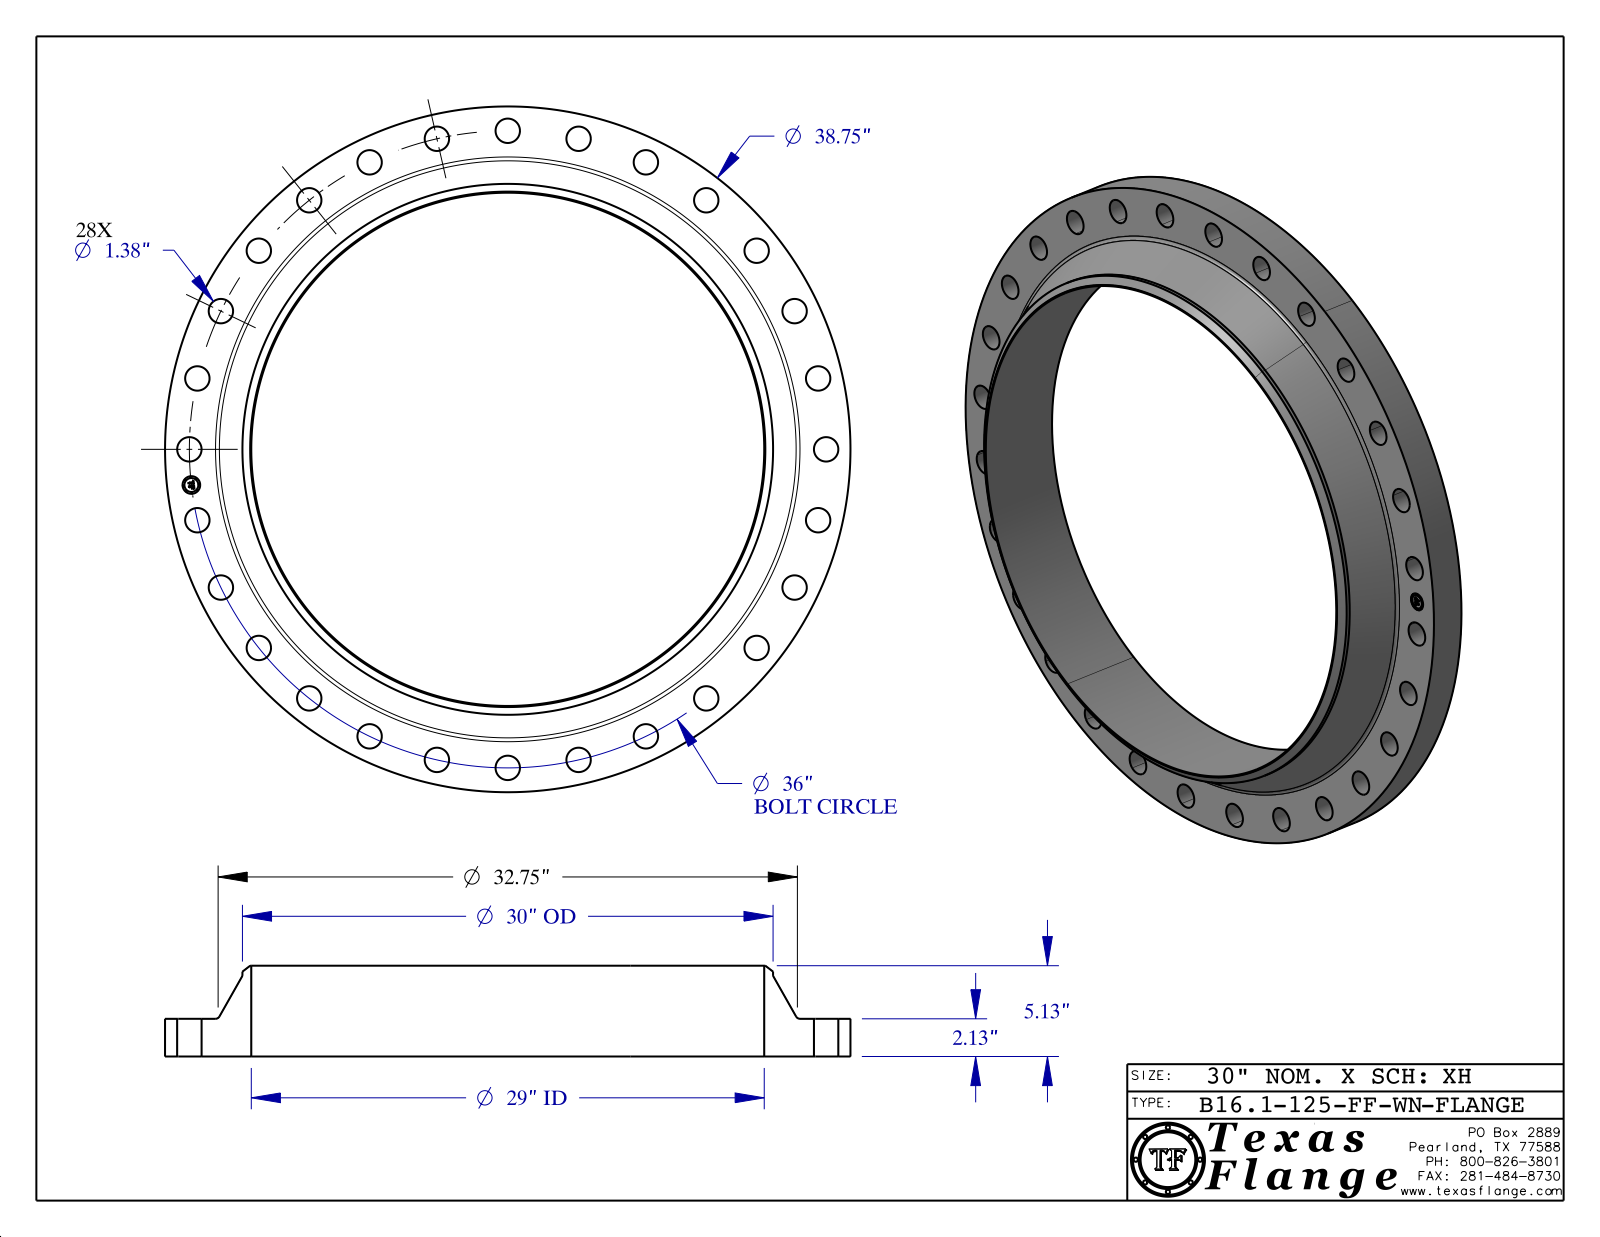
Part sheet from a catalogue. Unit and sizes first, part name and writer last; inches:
Units: inches
Overall size (bounding box): 38.75 × 38.75 × 5.13
Round holes (diameter × count): ⌀1.38 ×28, ⌀1 ×1, ⌀29 ×1
Round bosses / shafts (diameter × count): ⌀0.061 ×8, ⌀38.75 ×1, ⌀30 ×1, ⌀0.788 ×1
Main face-to-face distances: 2.13, 5.13, 3, 0.015, 2.115, 3.015, 0.298, 0.293, 0.054, 0.193
Hole centre spacings: 18, 19.153, 4.031, 8.011, 11.89, 15.62, 22.446, 25.456
Volume: 1 310 in³ · Surface area: 2 109 in²
Bodies: 1 solid, 456 faces (368 planar, 82 cylindrical, 6 other)
Part name (STEP PRODUCT): B16.1, Class 125-FF-WN
STEP written by: CATIA V5 STEP AP214 (AUTOMOTIVE_DESIGN)
